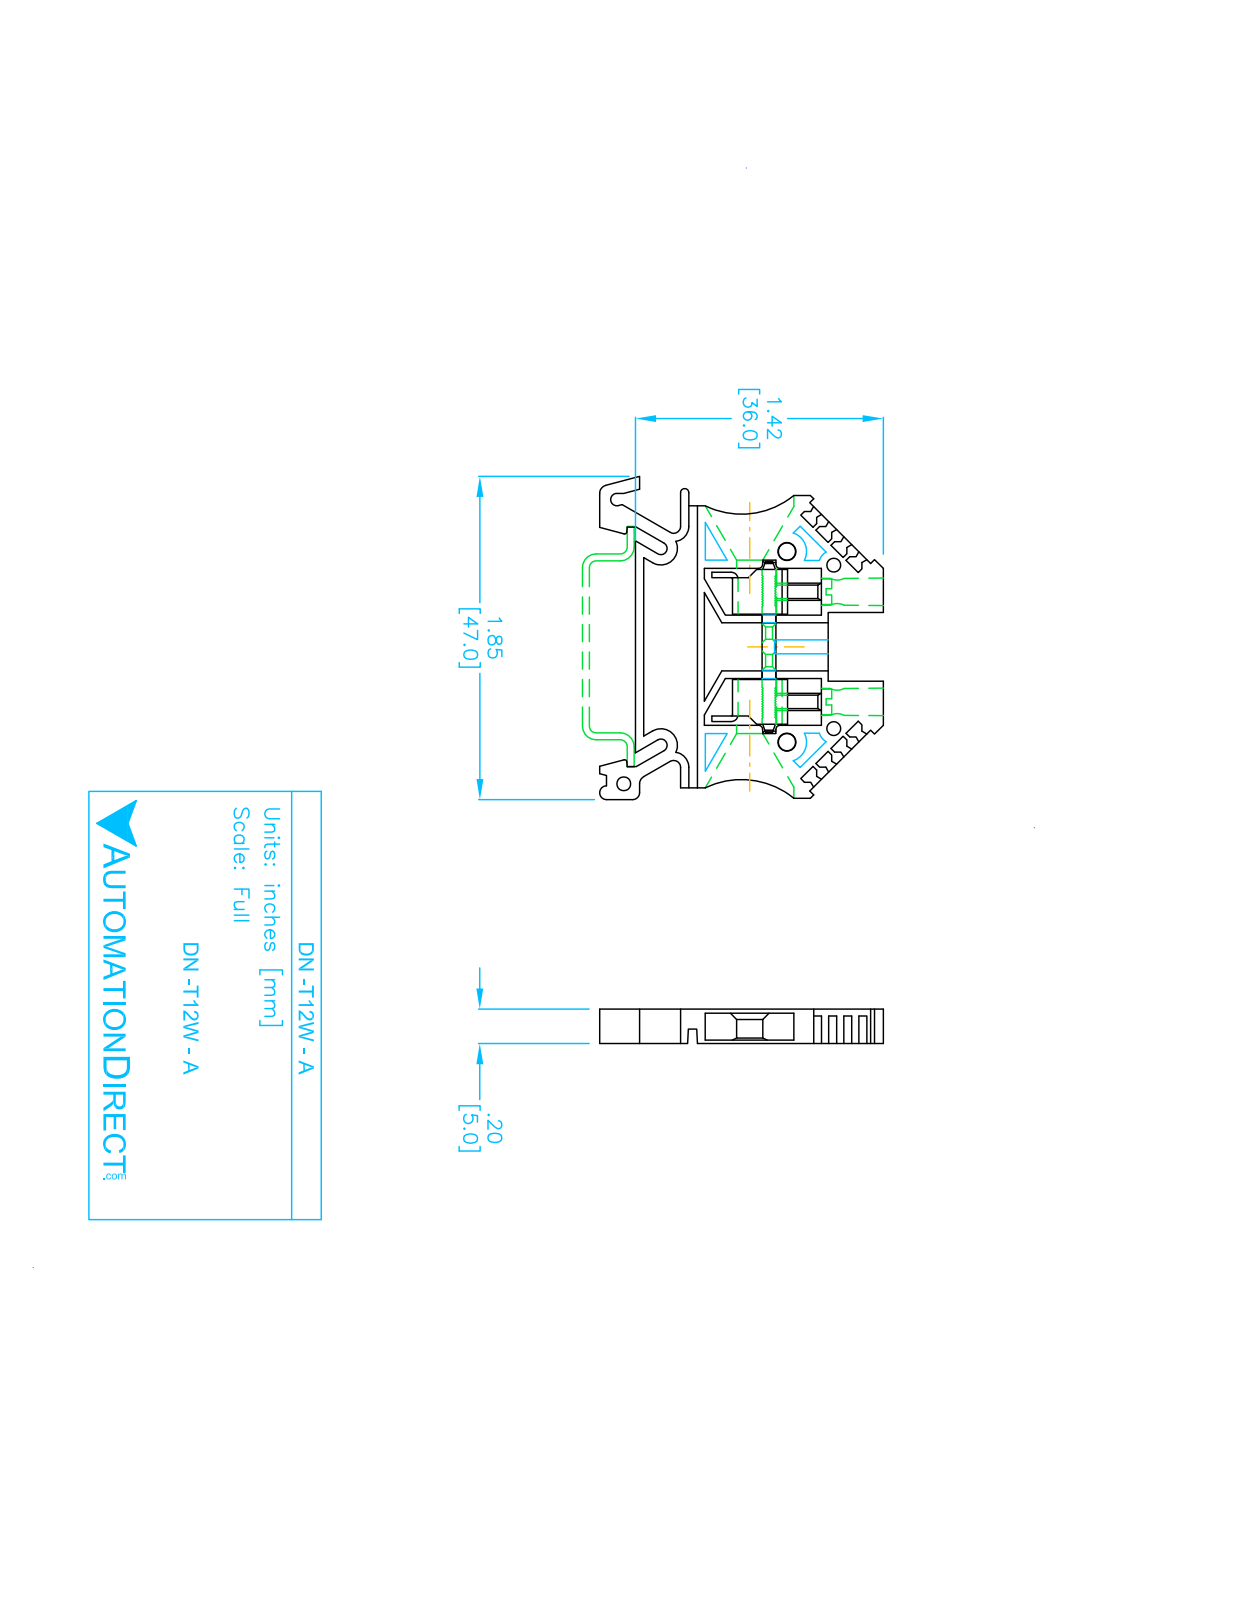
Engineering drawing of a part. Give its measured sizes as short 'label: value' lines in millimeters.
name: DN-T12W-A
written by: SolidWorks 2017 (AUTOMOTIVE_DESIGN)
unit: mm
bodies: 1 solid, 169 faces (134 planar, 35 cylindrical, 0 other)
size: 47 × 41.2 × 5
volume: 5 010 mm³; area: 4 601 mm²
holes: 2× ⌀4.2, 1× ⌀2
rounds: 4× R1, 3× R0.9, 2× R0.3, 2× R1.2, 2× R2.2, 2× R2.4, 2× R12, 1× R0.6
face distances: 4.8, 5, 2.2, 0.5, 2.7, 2.4, 2.9, 2.1, 2.6, 9
hole spacings: 15
